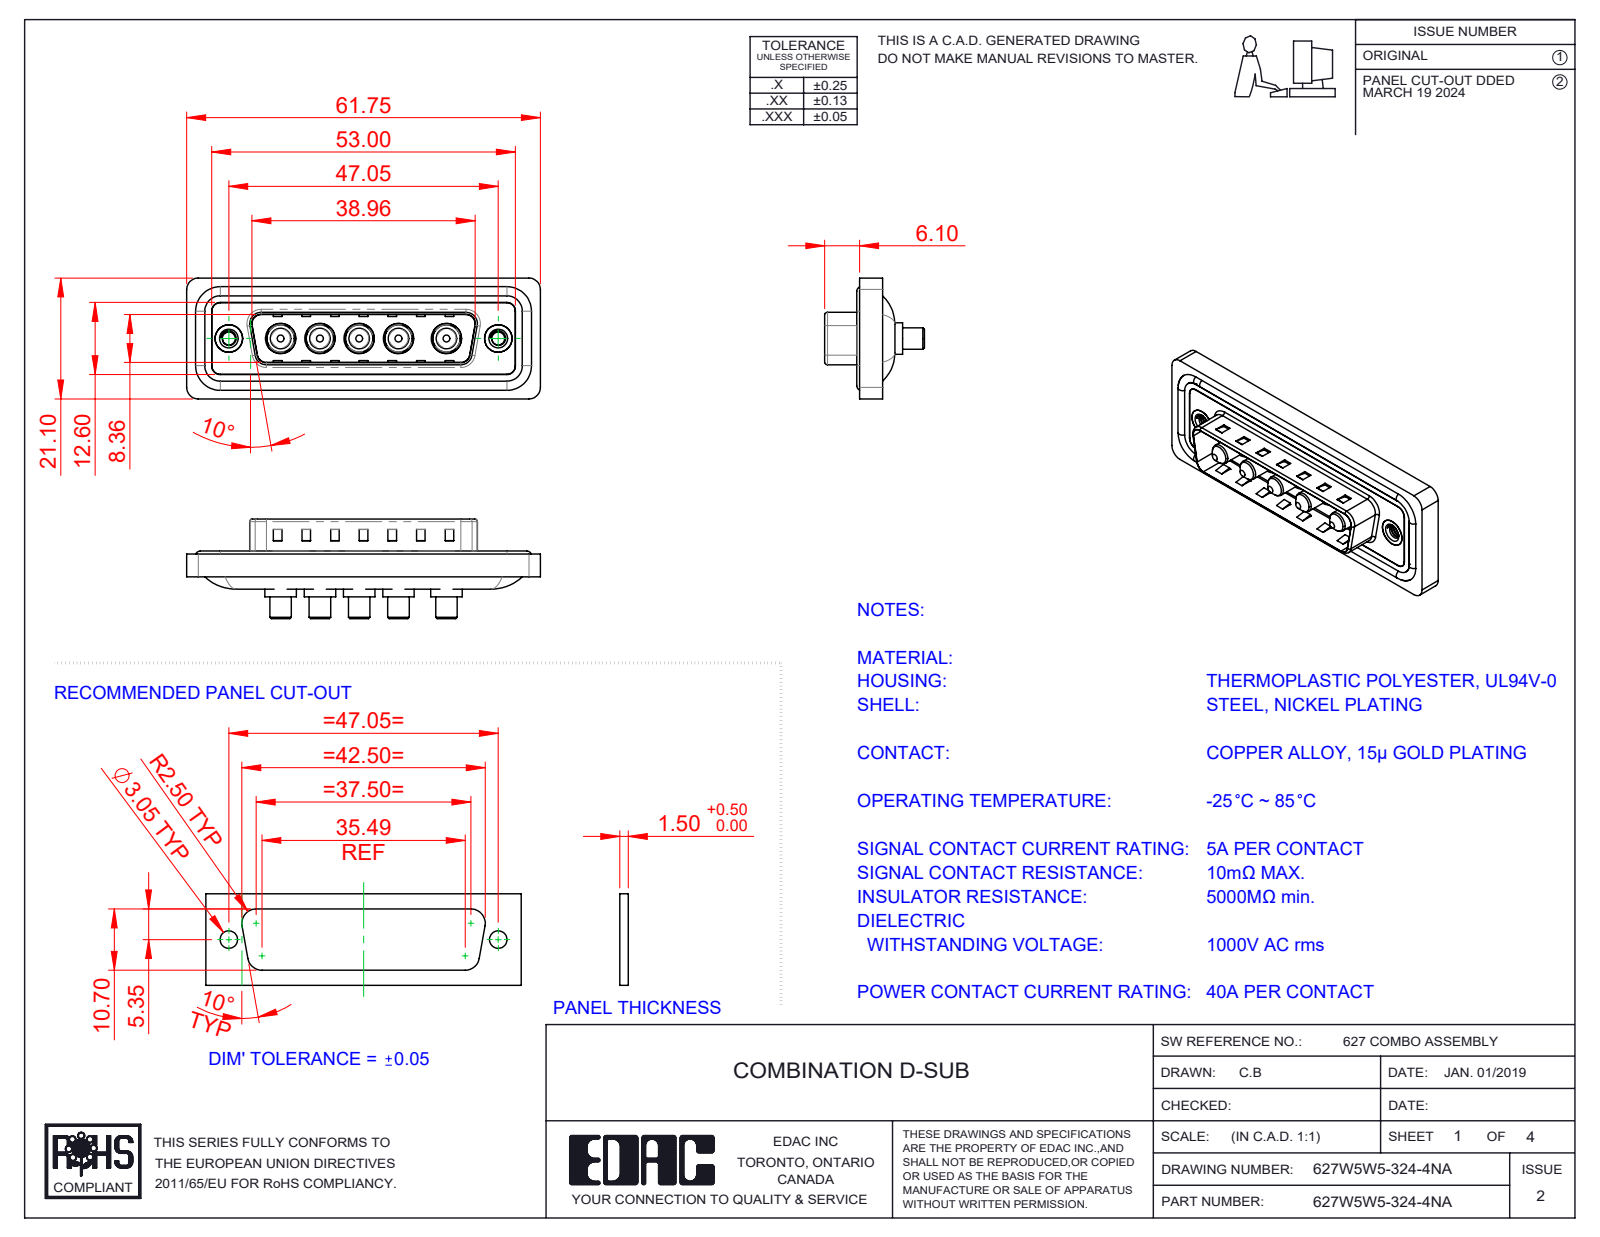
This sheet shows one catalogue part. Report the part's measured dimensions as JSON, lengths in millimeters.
{"part_name": "627W5W5-324-4NA; 627Combo Waterproof Housing_25 Contacts; 627Combo Shell Front_25 Contacts; 627Combo Threaded Rivet_A (+3 more)", "step_written_by": "SolidWorks 2023 (CONFIG_CONTROL_DESIGN)", "units": "millimeters", "bodies": {"solids": 17, "faces": 676, "planar": 259, "cylindrical": 285, "other": 132}, "overall_size": [61.75, 21.1, 17.4], "volume_mm3": 7567, "surface_area_mm2": 11848, "round_holes": [[4.85, 5], [5.3, 5], [2.26, 2], [4, 2], [4.8, 2], [5, 2]], "round_bosses_or_shafts": [[5.5, 5], [5.2, 5], [4.75, 5], [3.75, 5], [3.6, 5], [1.6, 4], [4.9, 2]], "partial_cylinders_radius": [[1.5, 22], [2, 18], [0.5, 8], [1.6, 8], [2.1, 5], [0.25, 4], [0.6, 4], [0.65, 4]], "face_to_face_distances": [0.4, 1.5, 0.5, 1.1, 3.1, 1.6, 2.9, 0.82, 9.58, 5.65], "hole_center_spacings": [6.86, 9.04, 13.73, 38.01, 6.87, 8.37, 8.38, 9.05]}
